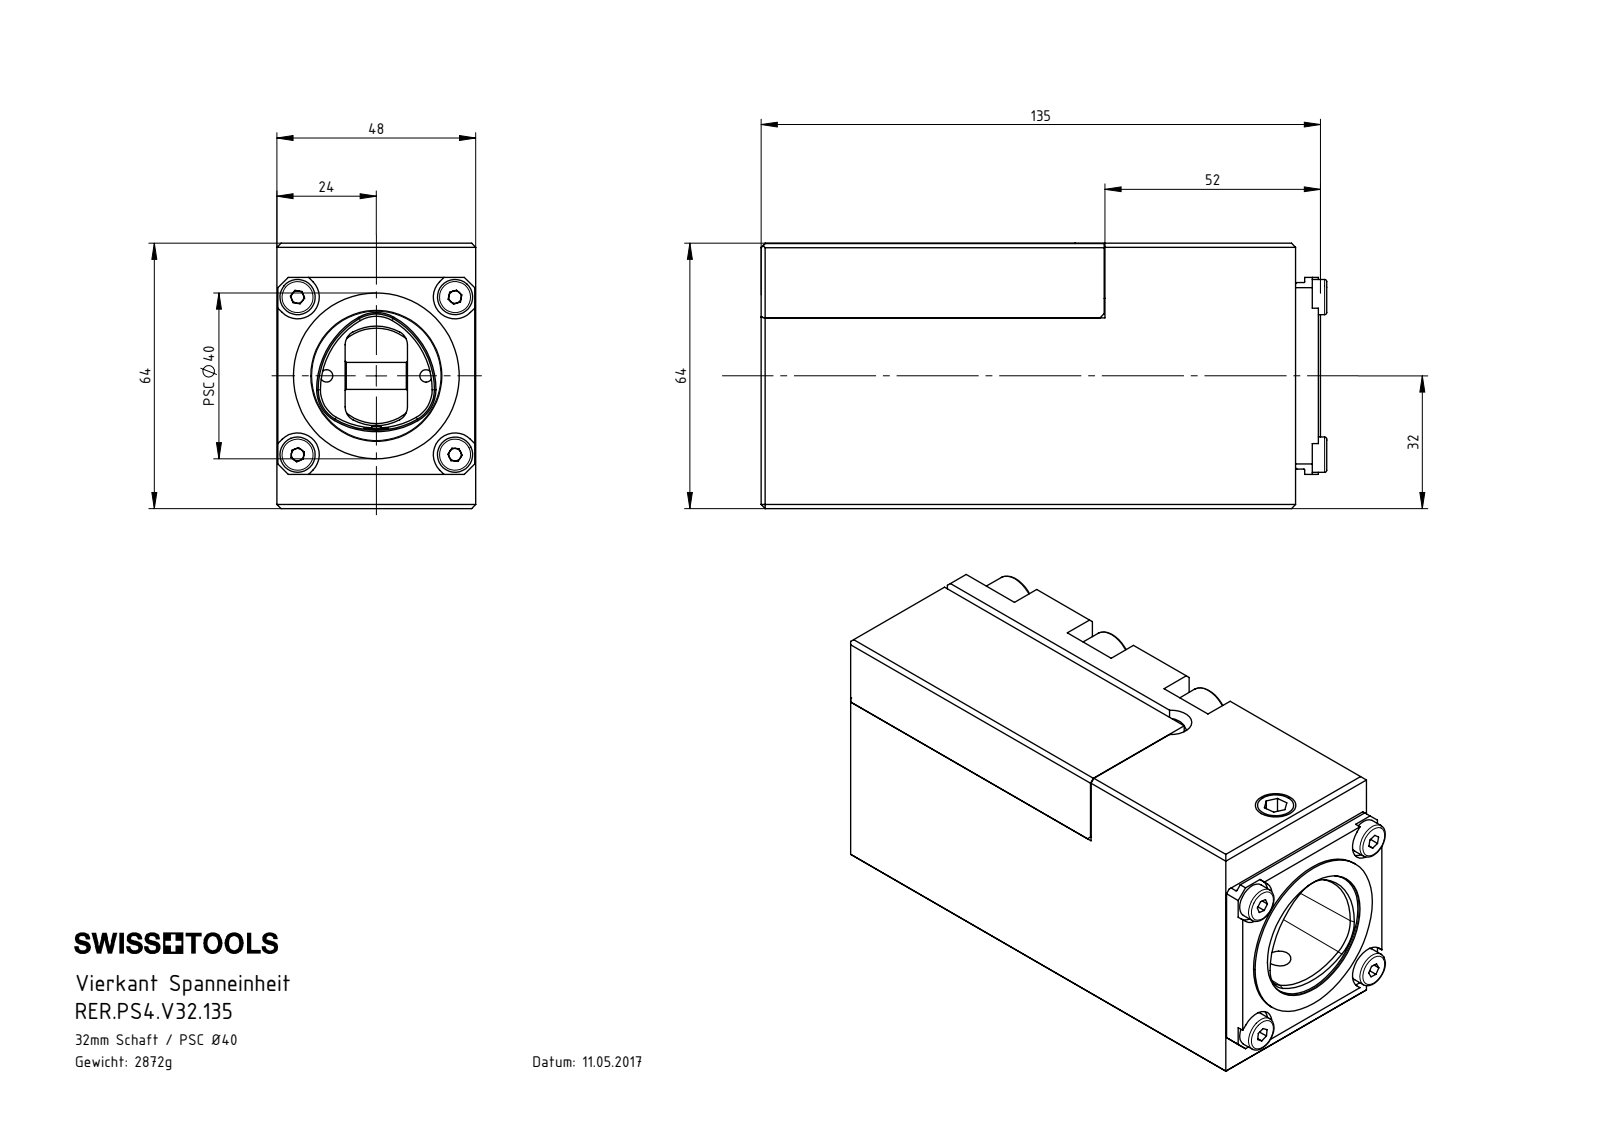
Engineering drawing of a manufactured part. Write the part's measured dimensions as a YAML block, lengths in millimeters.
part_name: "RER-ER1.V32.083_A; U40-PS4.ERx.010_A; U40-PS4.048.006; DIN 6325_ø3x10_2x6 (+8 more)"
step_written_by: "SolidWorks 2022 (AUTOMOTIVE_DESIGN)"
units: millimeters
bodies: {solids: 23, faces: 778, planar: 335, cylindrical: 172, other: 271}
overall_size: [136.5, 64, 48]
volume: 375114
surface_area: 81422
round_holes:
  - {diameter: 4.2, count: 4}
  - {diameter: 5.5, count: 4}
  - {diameter: 2.5, count: 3}
  - {diameter: 6.8, count: 3}
  - {diameter: 9, count: 3}
  - {diameter: 3, count: 2}
  - {diameter: 3.3, count: 2}
  - {diameter: 4, count: 1}
  - {diameter: 6, count: 1}
  - {diameter: 7, count: 1}
  - {diameter: 8.57, count: 1}
  - {diameter: 10.2, count: 1}
round_bosses_or_shafts:
  - {diameter: 8.5, count: 4}
  - {diameter: 8, count: 4}
  - {diameter: 5, count: 4}
  - {diameter: 13, count: 3}
  - {diameter: 5.5, count: 2}
  - {diameter: 3, count: 2}
  - {diameter: 40, count: 1}
  - {diameter: 39.7, count: 1}
partial_cylinders:
  - {radius: 3.5, count: 4}
  - {radius: 5.25, count: 4}
  - {radius: 7.5, count: 3}
  - {radius: 0.2, count: 2}
  - {radius: 2.75, count: 2}
  - {radius: 3, count: 2}
  - {radius: 9, count: 1}
  - {radius: 12, count: 1}
face_to_face_distances: [48, 64, 63.91, 129, 2, 42, 87, 47.5, 16.5, 34]
hole_center_spacings: [33, 20.25, 26.87, 36.36, 38, 66, 12, 12.69]
